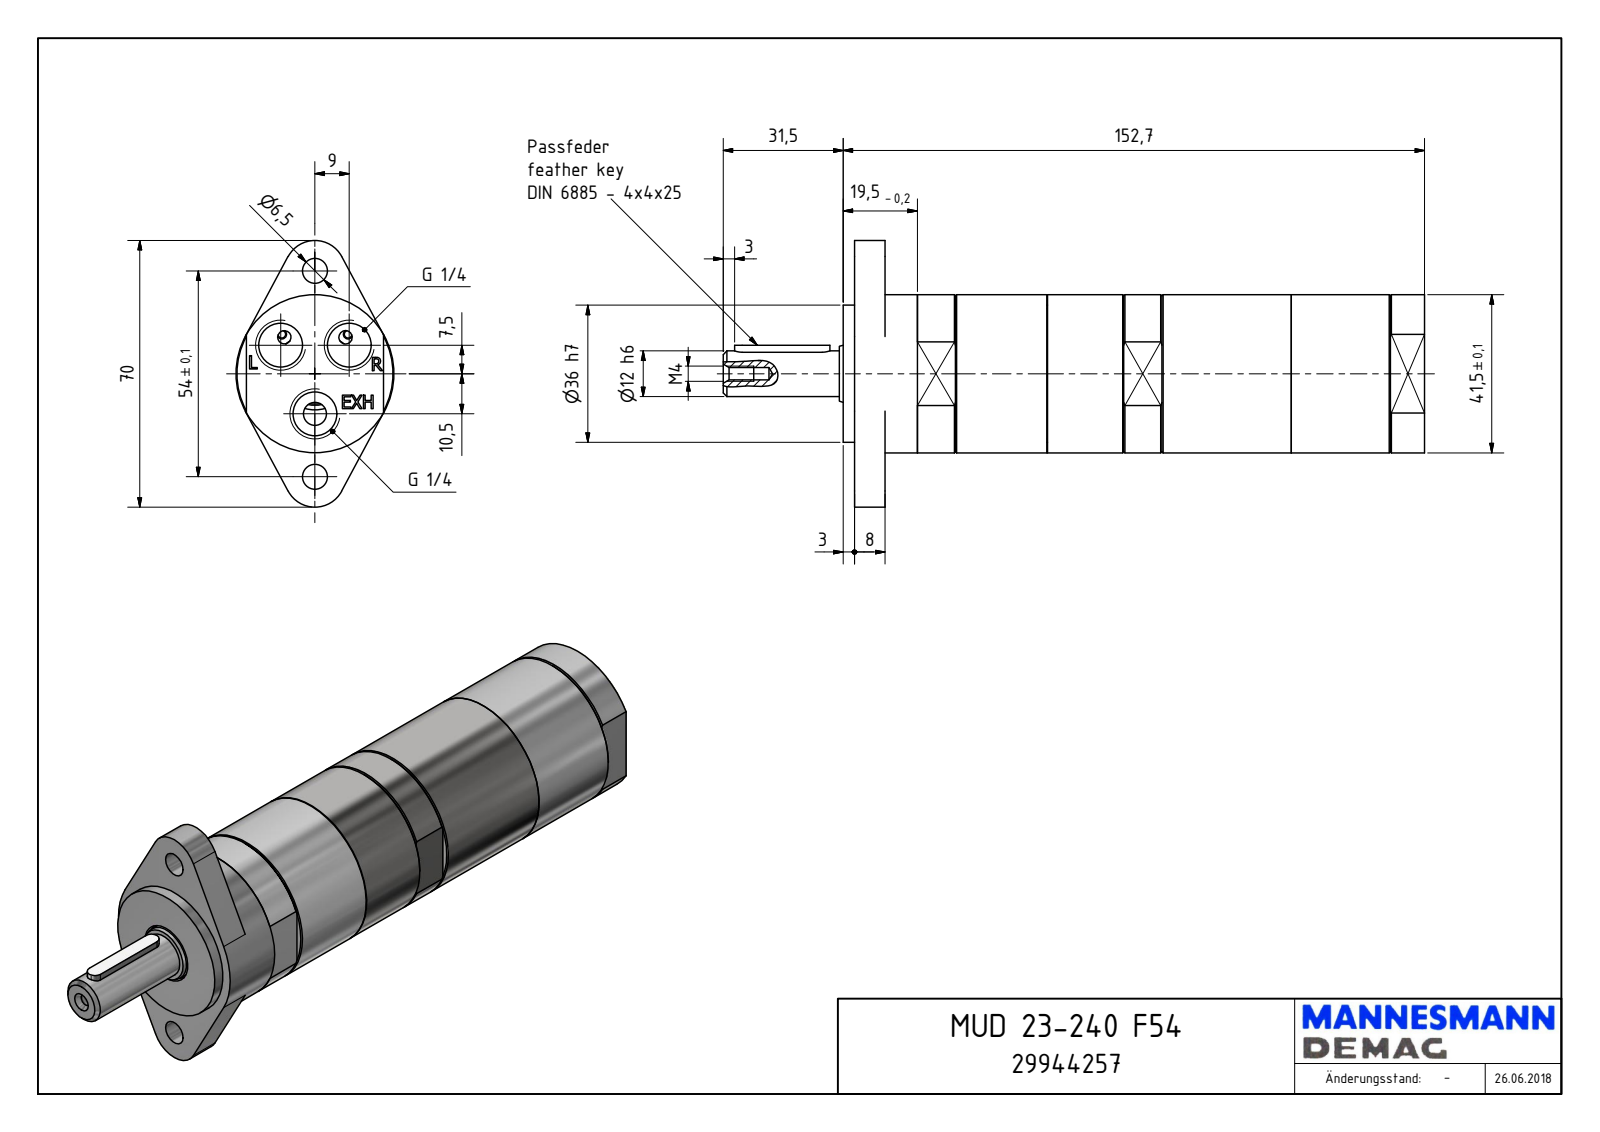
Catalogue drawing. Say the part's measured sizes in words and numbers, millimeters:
The part is named "MUD 23-240 F54_29944257". Its 3-D file was written by "Autodesk Inventor 2018 (AUTOMOTIVE_DESIGN)". It is 1 solid with 153 faces: 97 planar, 27 cylindrical and 29 other. Overall it measures 184.2 by 70 by 41.5 millimeters. Its volume is 208 281 cubic millimeters and its surface area 27 763 square millimeters. Round holes: 3 of diameter 11.45, 2 of diameter 6.5, 1 of diameter 3.24, 1 of diameter 16, 1 of diameter 23. Round bosses or shafts: 1 of diameter 41.5, 1 of diameter 37.71, 1 of diameter 36, 1 of diameter 14.95, 1 of diameter 12. Partial cylindrical surfaces (rounded edges, fillets, slot ends): 2 of radius 2, 2 of radius 8. The main face-to-face distances are 3, 149.7, 152.7, 141.7, 8, 11, 1, 41.48, 37, 38. The hole center spacings are 11.72, 20.12, 21.48, 27, 35.65, 10.5, 16.5, 18.
